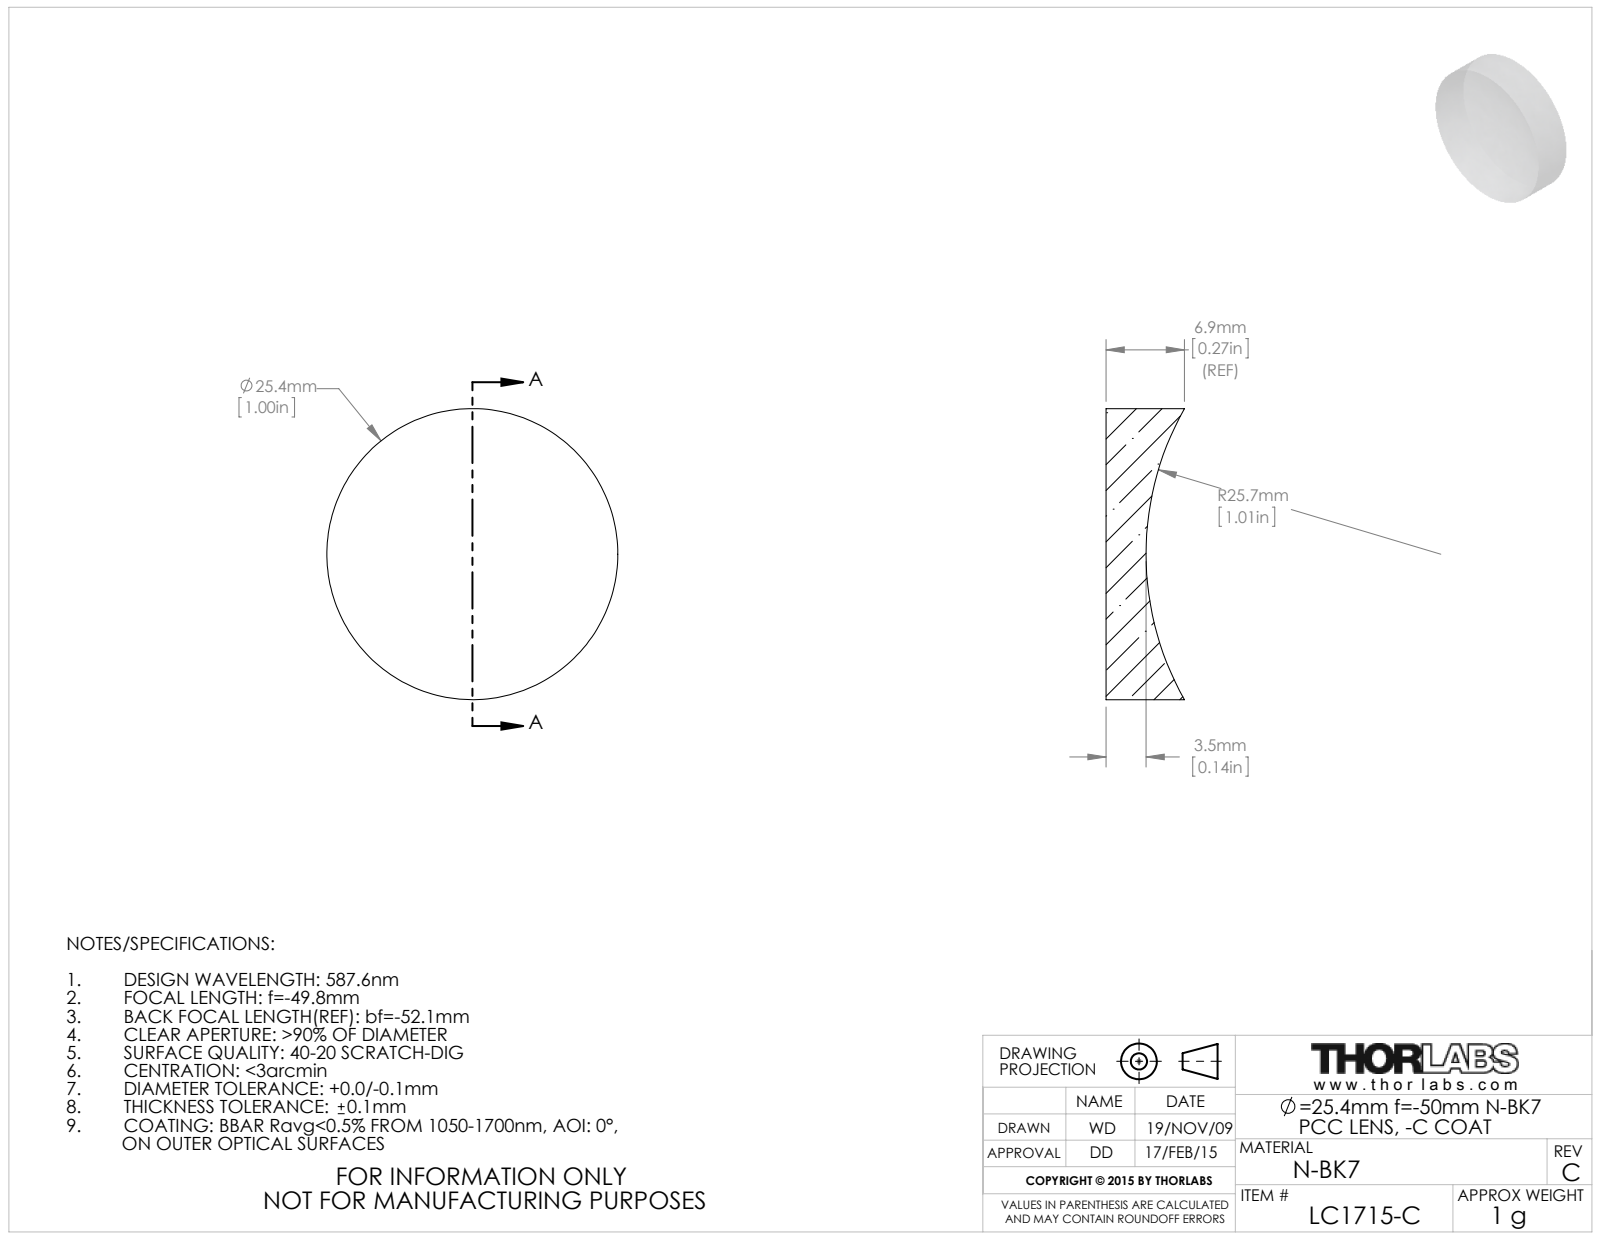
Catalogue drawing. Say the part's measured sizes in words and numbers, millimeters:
The part is named "4804-E0W". Its 3-D file was written by "SolidWorks 2009 (AUTOMOTIVE_DESIGN)". It is 1 solid with 5 faces: 1 planar, 2 cylindrical and 2 other. Overall it measures 25.4 by 25.4 by 6.85 millimeters. Its volume is 2 603 cubic millimeters and its surface area 1 596 square millimeters. Round bosses or shafts: 1 of diameter 25.4.
